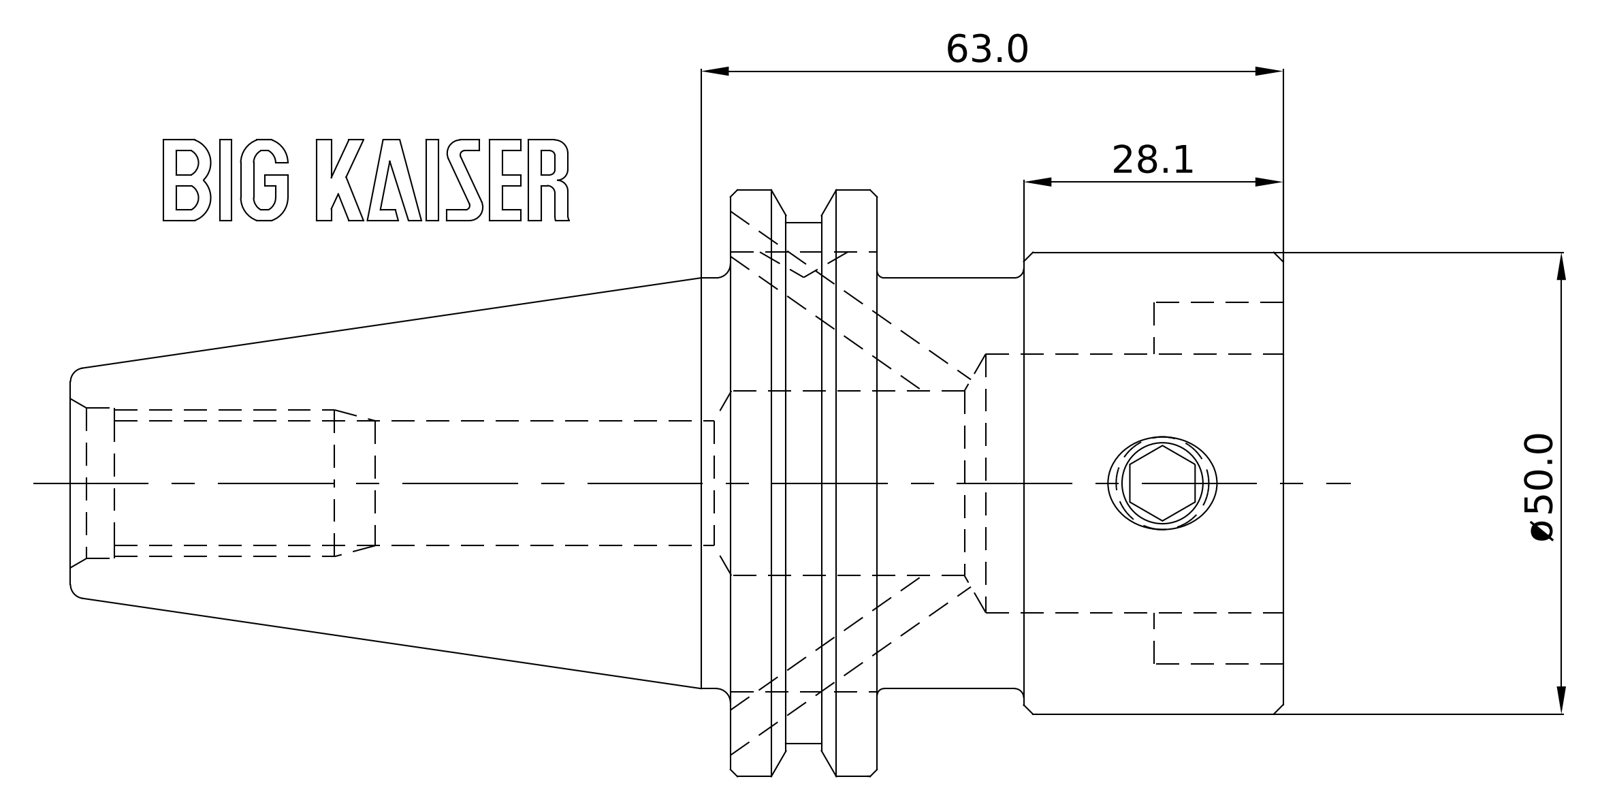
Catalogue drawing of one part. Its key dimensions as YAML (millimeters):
part_name: "11.326.851"
step_written_by: "SolidWorks 2021 (CONFIG_CONTROL_DESIGN)"
units: millimeters
bodies: {solids: 1, faces: 16, planar: 7, cylindrical: 6, other: 3}
overall_size: [131.25, 63.5, 63.5]
volume: 197024
surface_area: 24572
round_bosses_or_shafts:
  - {diameter: 63.5, count: 1}
  - {diameter: 56.36, count: 1}
  - {diameter: 50, count: 1}
  - {diameter: 44.45, count: 1}
face_to_face_distances: [59.83, 43.95, 15.88, 131.25, 87.3, 71.42, 27.95, 16, 31.88, 103.3]
